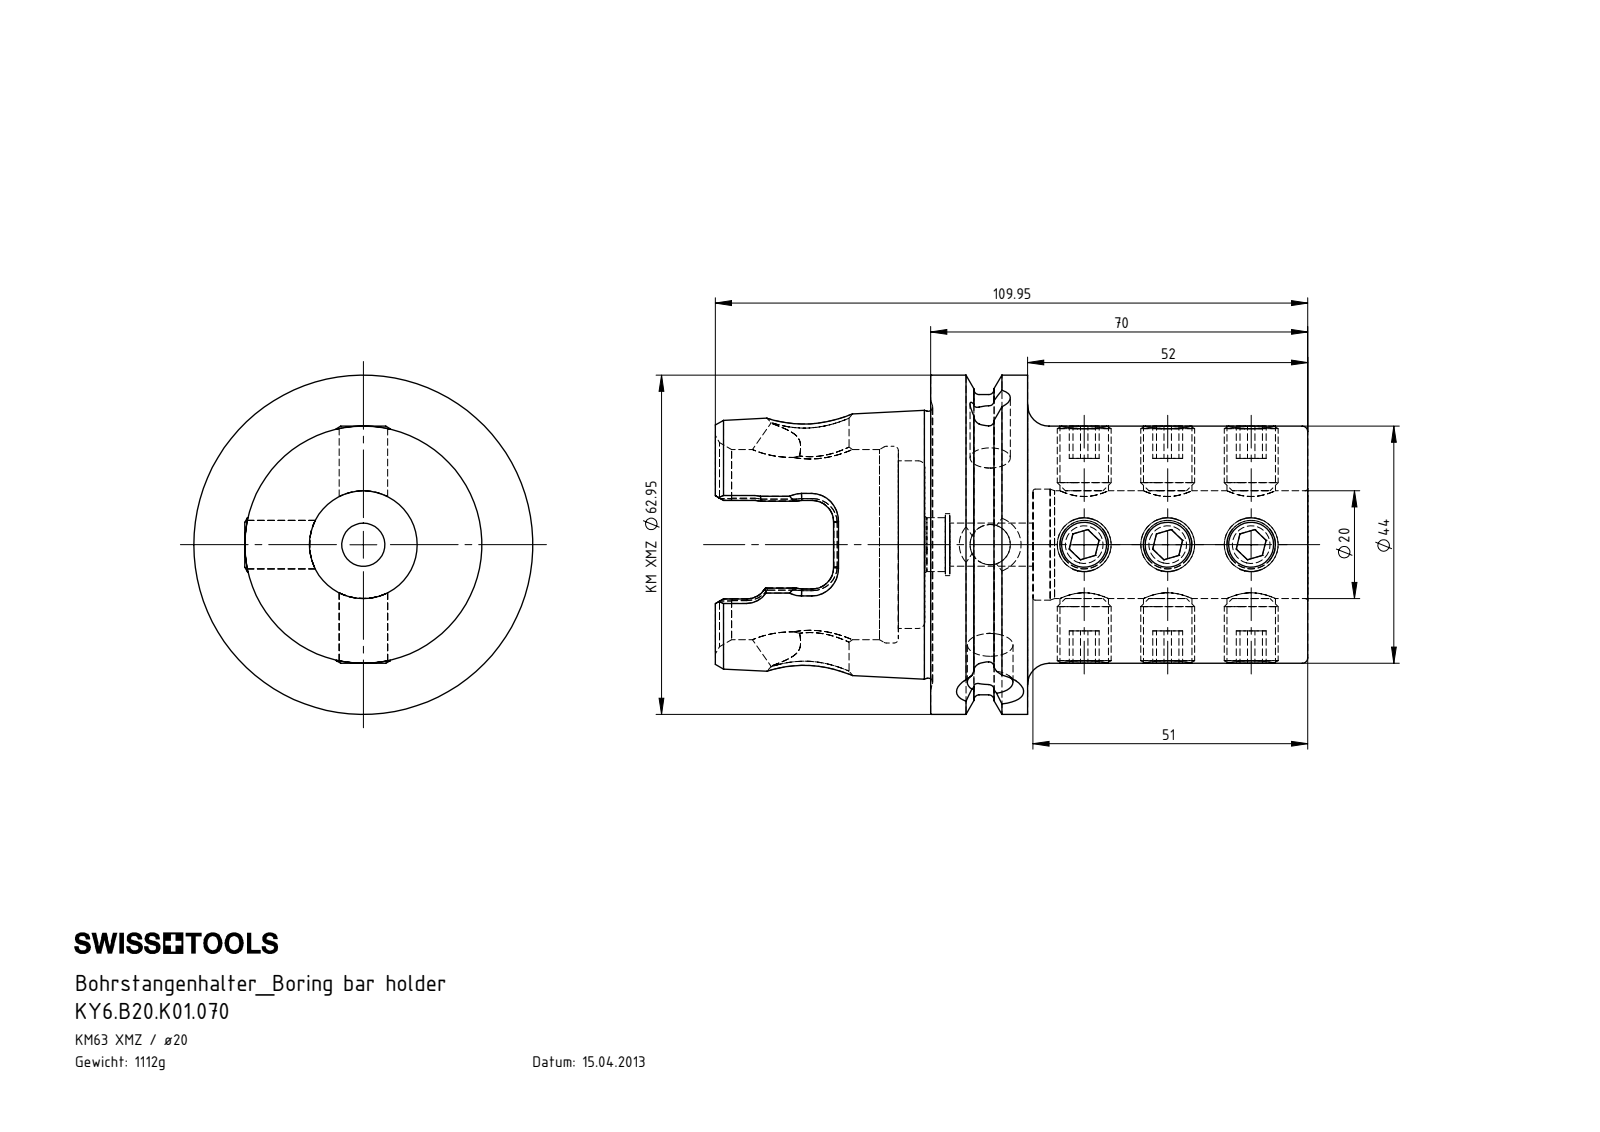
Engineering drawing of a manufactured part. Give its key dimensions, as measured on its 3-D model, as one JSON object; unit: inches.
{"part_name": "KY6-B20.K01.070; ISO 4026 - M10 x 12_PreviewCfg; KY6-B20.K01.070_A", "step_written_by": "SolidWorks 2012 (CONFIG_CONTROL_DESIGN)", "units": "inches", "bodies": {"solids": 10, "faces": 370, "planar": 127, "cylindrical": 88, "other": 155}, "overall_size": [4.329, 2.478, 2.478], "volume_in3": 8.641, "surface_area_in2": 58.31, "round_holes": [[0.354, 6], [0.294, 2], [0.315, 1], [0.334, 1], [0.394, 1], [0.453, 1], [0.571, 1], [0.787, 1], [0.811, 1], [1.224, 1], [1.389, 1], [1.437, 1]], "round_bosses_or_shafts": [[0.394, 6], [2.478, 1], [2.193, 1], [1.732, 1]], "partial_cylinders_radius": [[0.157, 6], [0.277, 2]], "face_to_face_distances": [2.047, 0.709, 2.756, 0.236, 0.043, 0.752, 2.799, 0.197, 0.472, 1.26], "hole_center_spacings": [0.61, 1.22, 0.687, 1.297, 1.907, 2.004, 2.614, 3.224]}
